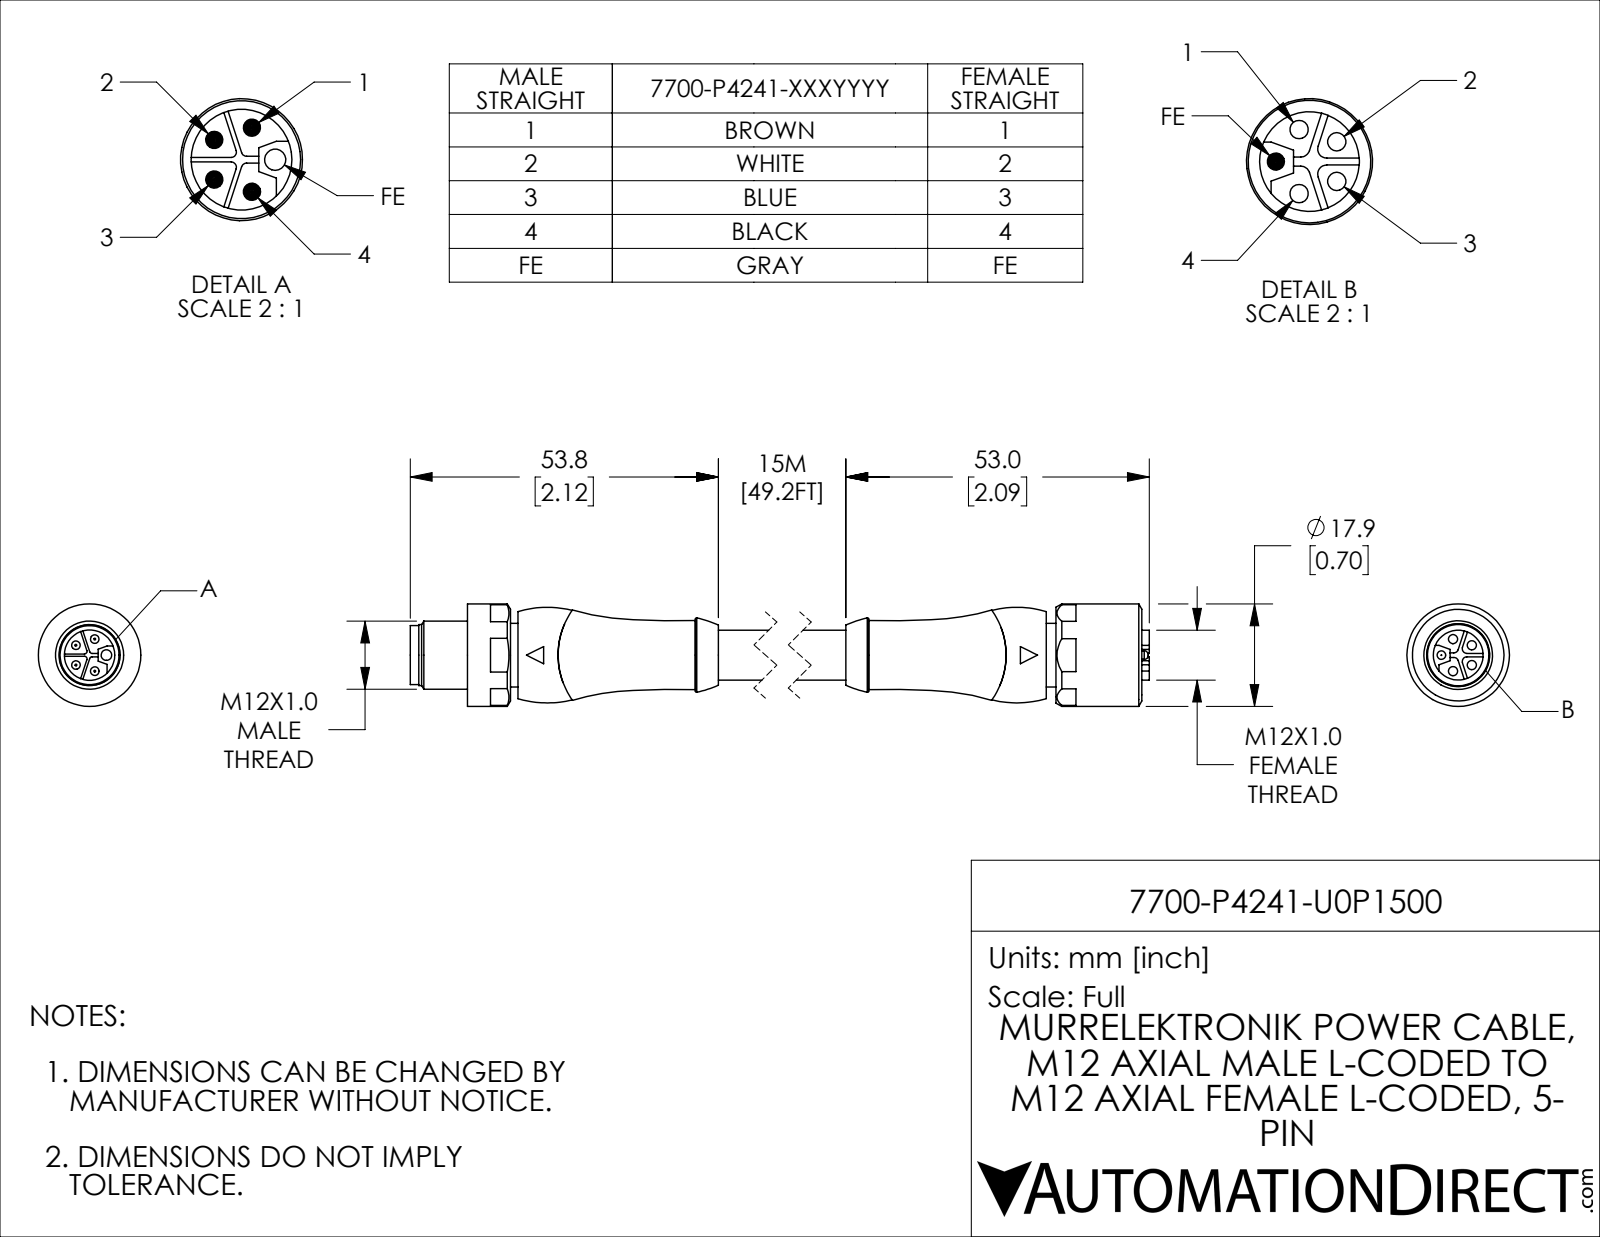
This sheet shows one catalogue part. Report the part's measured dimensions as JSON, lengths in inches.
{"part_name": "7700-P4241-U0P1500_1; 7700-P4241-U0P1500_2; 7700-P4241-U0P1500", "step_written_by": "SolidWorks 2021 (CONFIG_CONTROL_DESIGN)", "units": "inches", "bodies": {"solids": 3, "faces": 214, "planar": 98, "cylindrical": 62, "other": 54}, "overall_size": [5.386, 0.705, 0.705], "volume_in3": 1.09, "surface_area_in2": 14.44, "round_holes": [[0.063, 4], [0.073, 1], [0.346, 1], [0.433, 1], [0.512, 1]], "round_bosses_or_shafts": [[0.059, 5], [0.705, 1], [0.51, 1], [0.469, 1], [0.437, 1], [0.419, 1], [0.406, 1], [0.343, 1]], "partial_cylinders_radius": [[0.018, 4], [0.031, 4]], "face_to_face_distances": [4.283, 0.067, 0.346, 0.666, 0.051, 0.295, 0.228, 4.941, 0.657, 4.35], "hole_center_spacings": [0.116, 0.136, 0.22, 0.22]}
